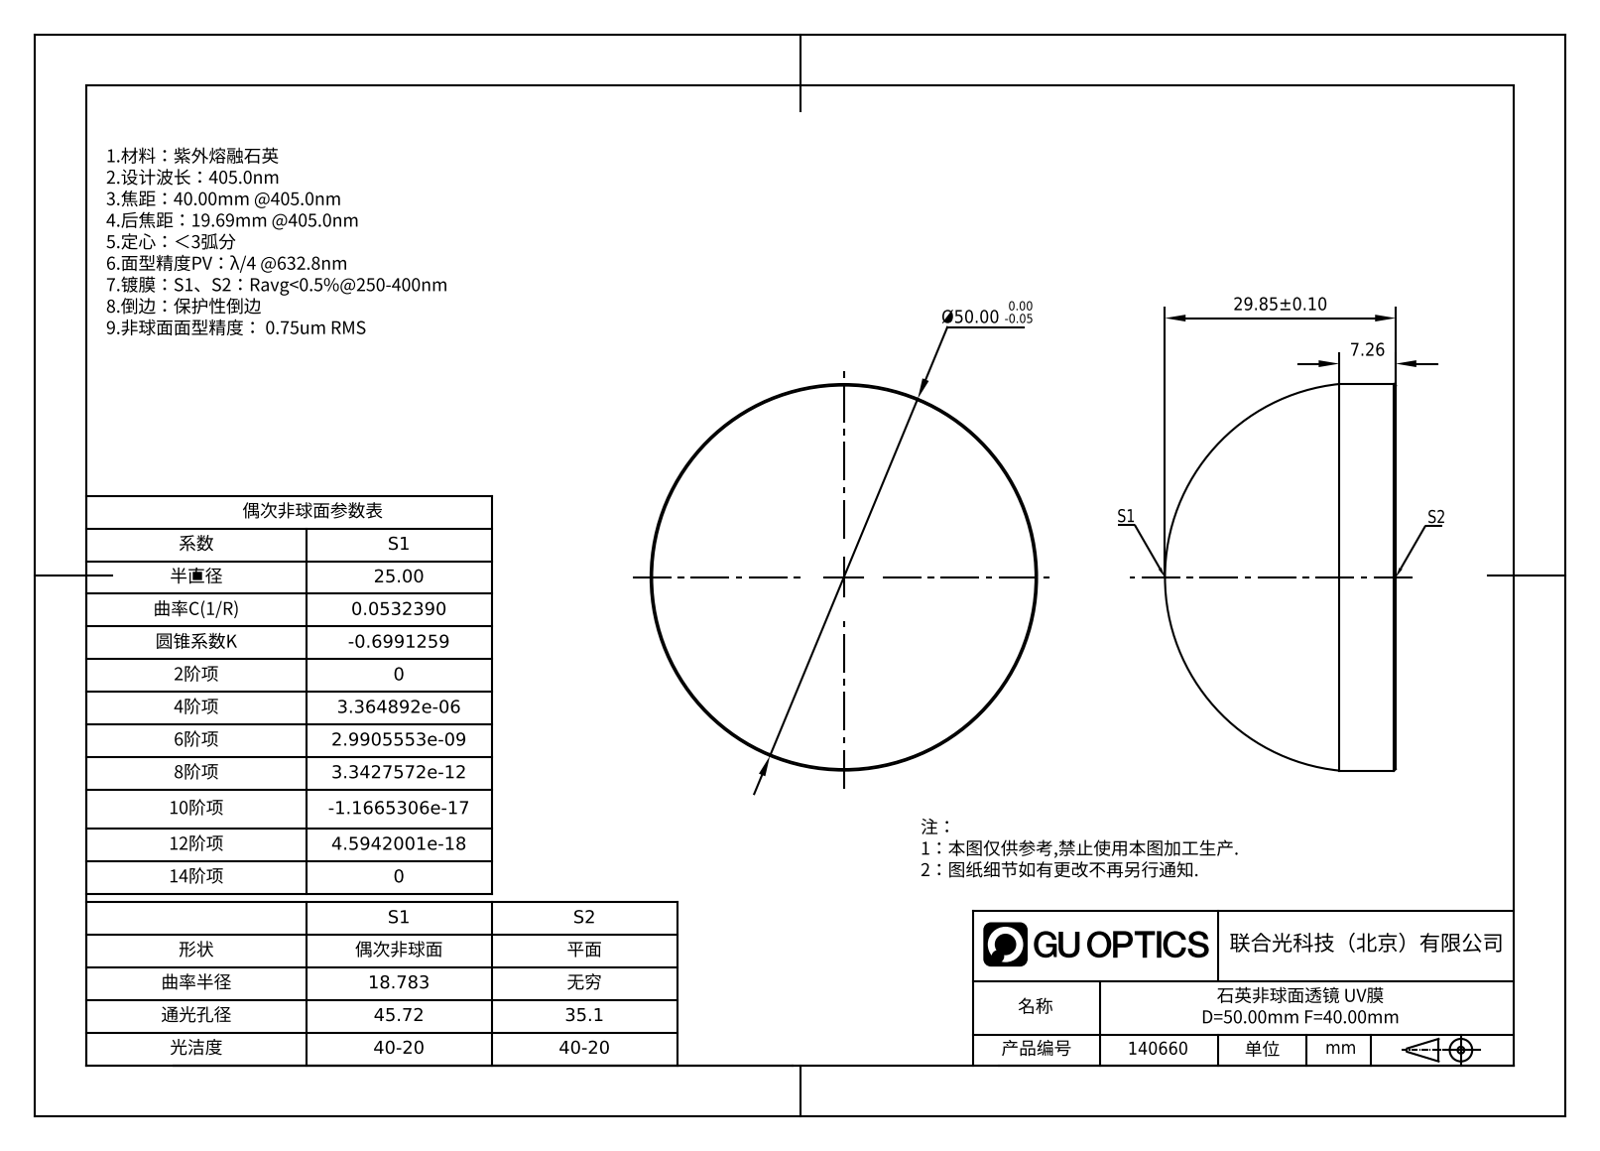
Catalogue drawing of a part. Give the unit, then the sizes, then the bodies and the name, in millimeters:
Units: millimetres
Overall size (bounding box): 50 × 50 × 29.85
Round bosses / shafts (diameter × count): ⌀50 ×1
Volume: 42 470 mm³ · Surface area: 6 652 mm²
Bodies: 1 solid, 7 faces (1 planar, 2 cylindrical, 4 other)
Part name (STEP PRODUCT): GLA21-050-040-UV
STEP written by: SolidWorks 2022 (AUTOMOTIVE_DESIGN)
